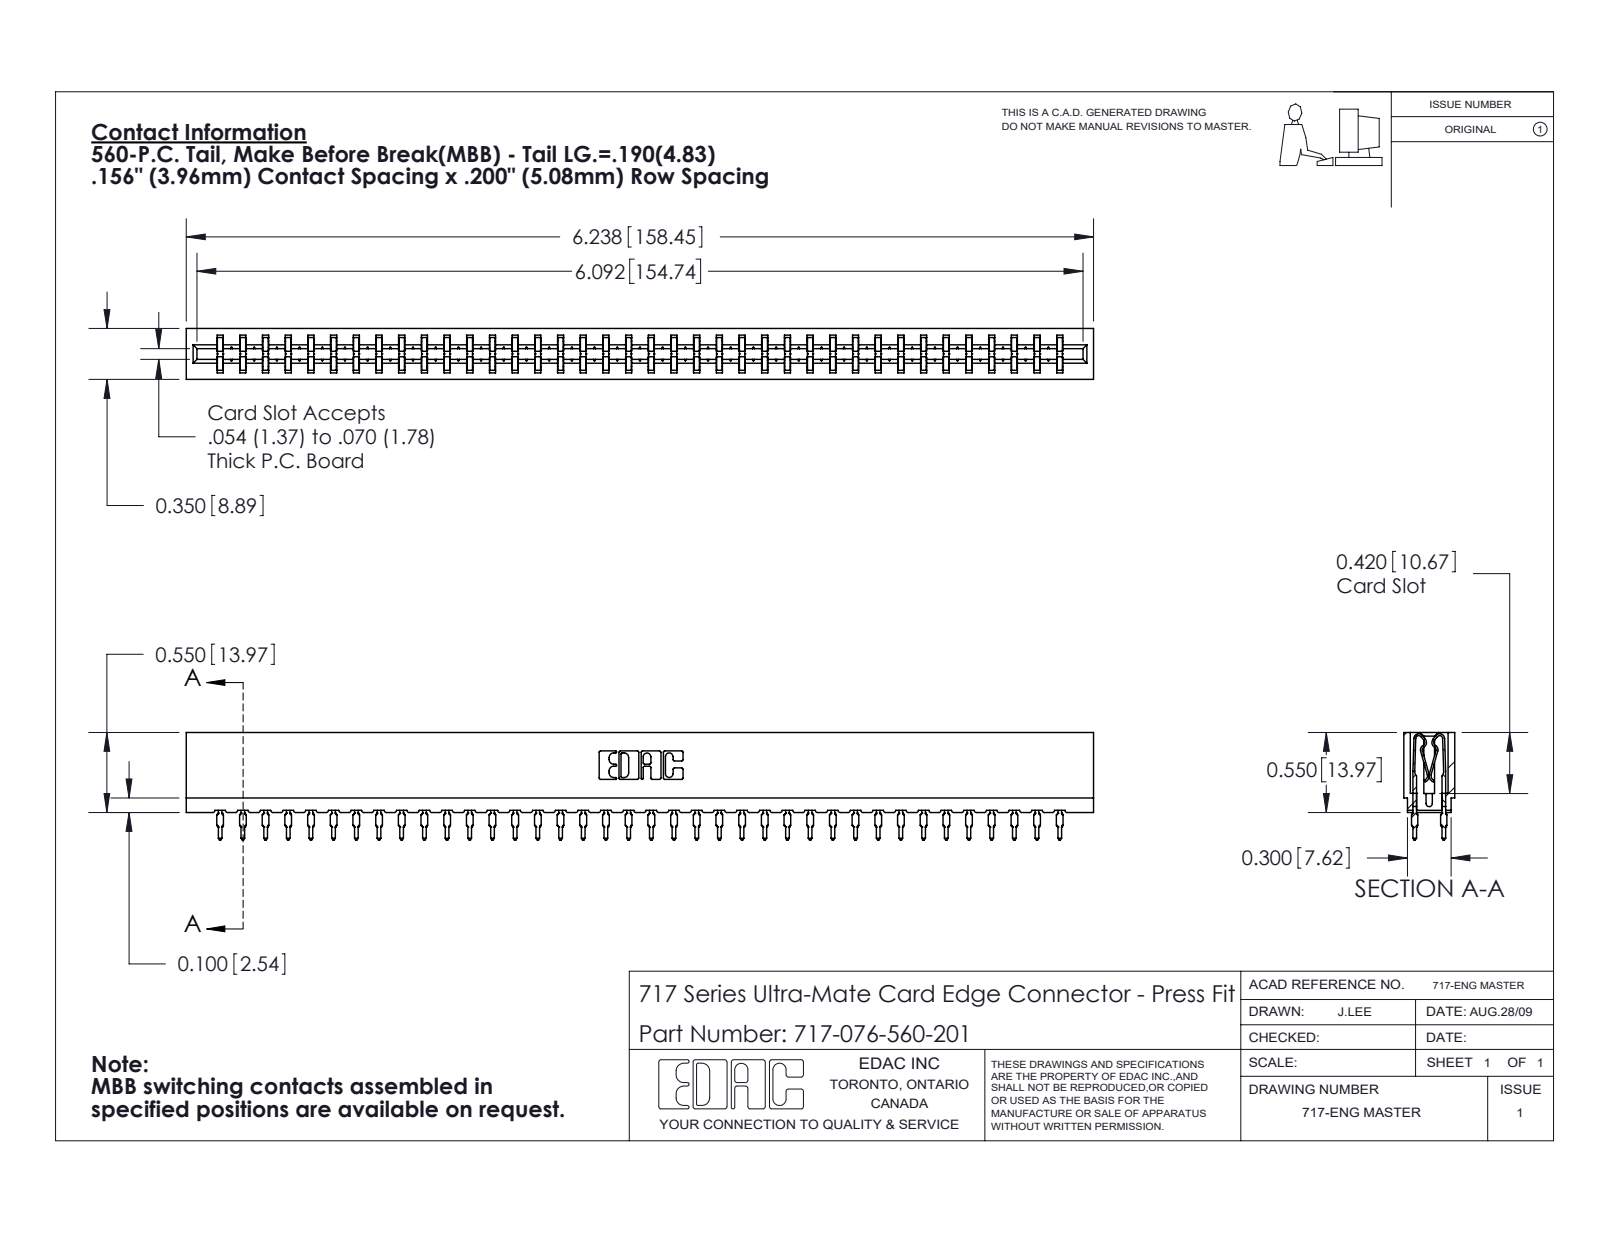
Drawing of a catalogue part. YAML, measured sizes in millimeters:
part_name: "745-292-001_560; 717-076-560-201; 717 Part_Insulator Option - 06"
step_written_by: "SolidWorks 2020 (CONFIG_CONTROL_DESIGN)"
units: millimeters
bodies: {solids: 77, faces: 7618, planar: 3968, cylindrical: 1674, other: 1976}
overall_size: [158.4, 18.8, 8.9]
volume: 14000
surface_area: 22740
partial_cylinders:
  - {radius: 0.5, count: 152}
  - {radius: 0.4, count: 76}
  - {radius: 0.3, count: 22}
  - {radius: 0.1, count: 8}
  - {radius: 0.3, count: 8}
  - {radius: 0.2, count: 6}
  - {radius: 0.8, count: 6}
  - {radius: 0.7, count: 3}
face_to_face_distances: [5.4, 3.5, 8.9, 1.6, 7.3, 1.9, 3.8, 1.9, 1.1, 7.7]
